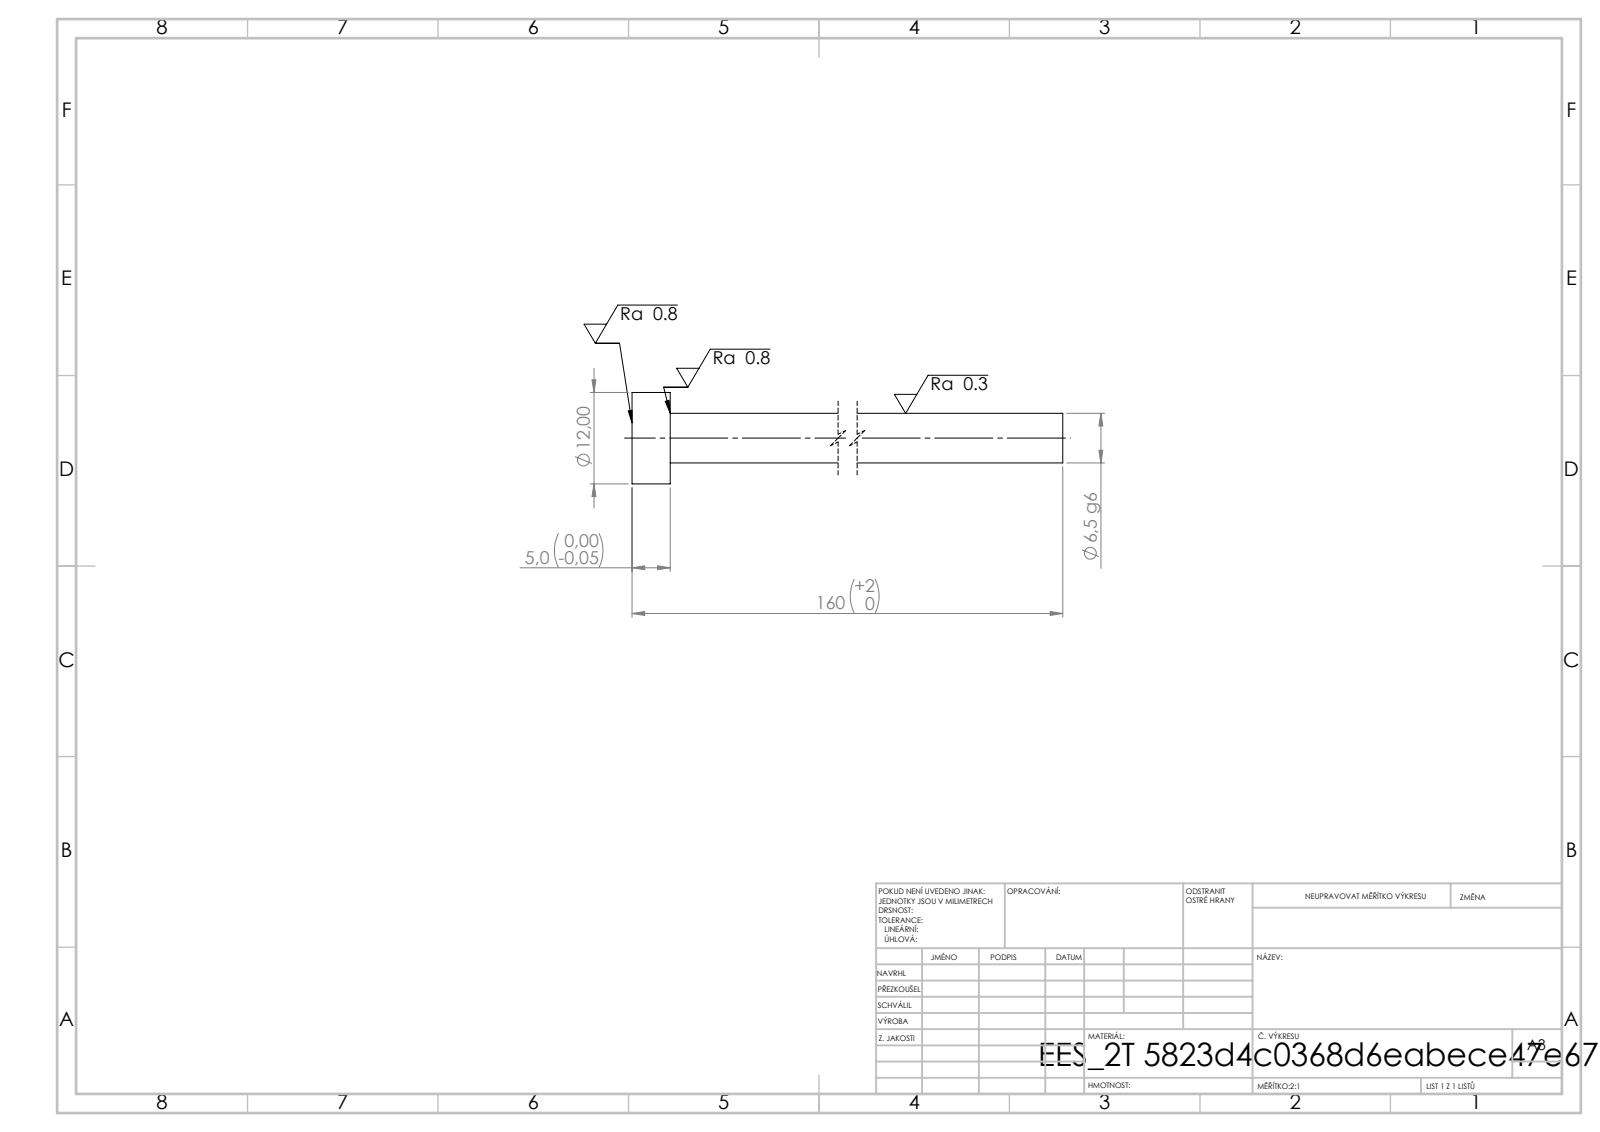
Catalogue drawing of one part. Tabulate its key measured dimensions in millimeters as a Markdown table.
| quantity | value |
| --- | --- |
| STEP written by | SolidWorks 2019 (CONFIG_CONTROL_DESIGN) |
| units | millimeters |
| bodies | 1 solid, 7 faces (3 planar, 4 cylindrical, 0 other) |
| overall size | 160 × 12 × 12 |
| volume | 5 709 mm³ |
| surface area | 3 580 mm² |
| round bosses / shafts (diameter × count) | 12 × 1, 6.5 × 1 |
| main face-to-face distances | 5, 160, 155 |
